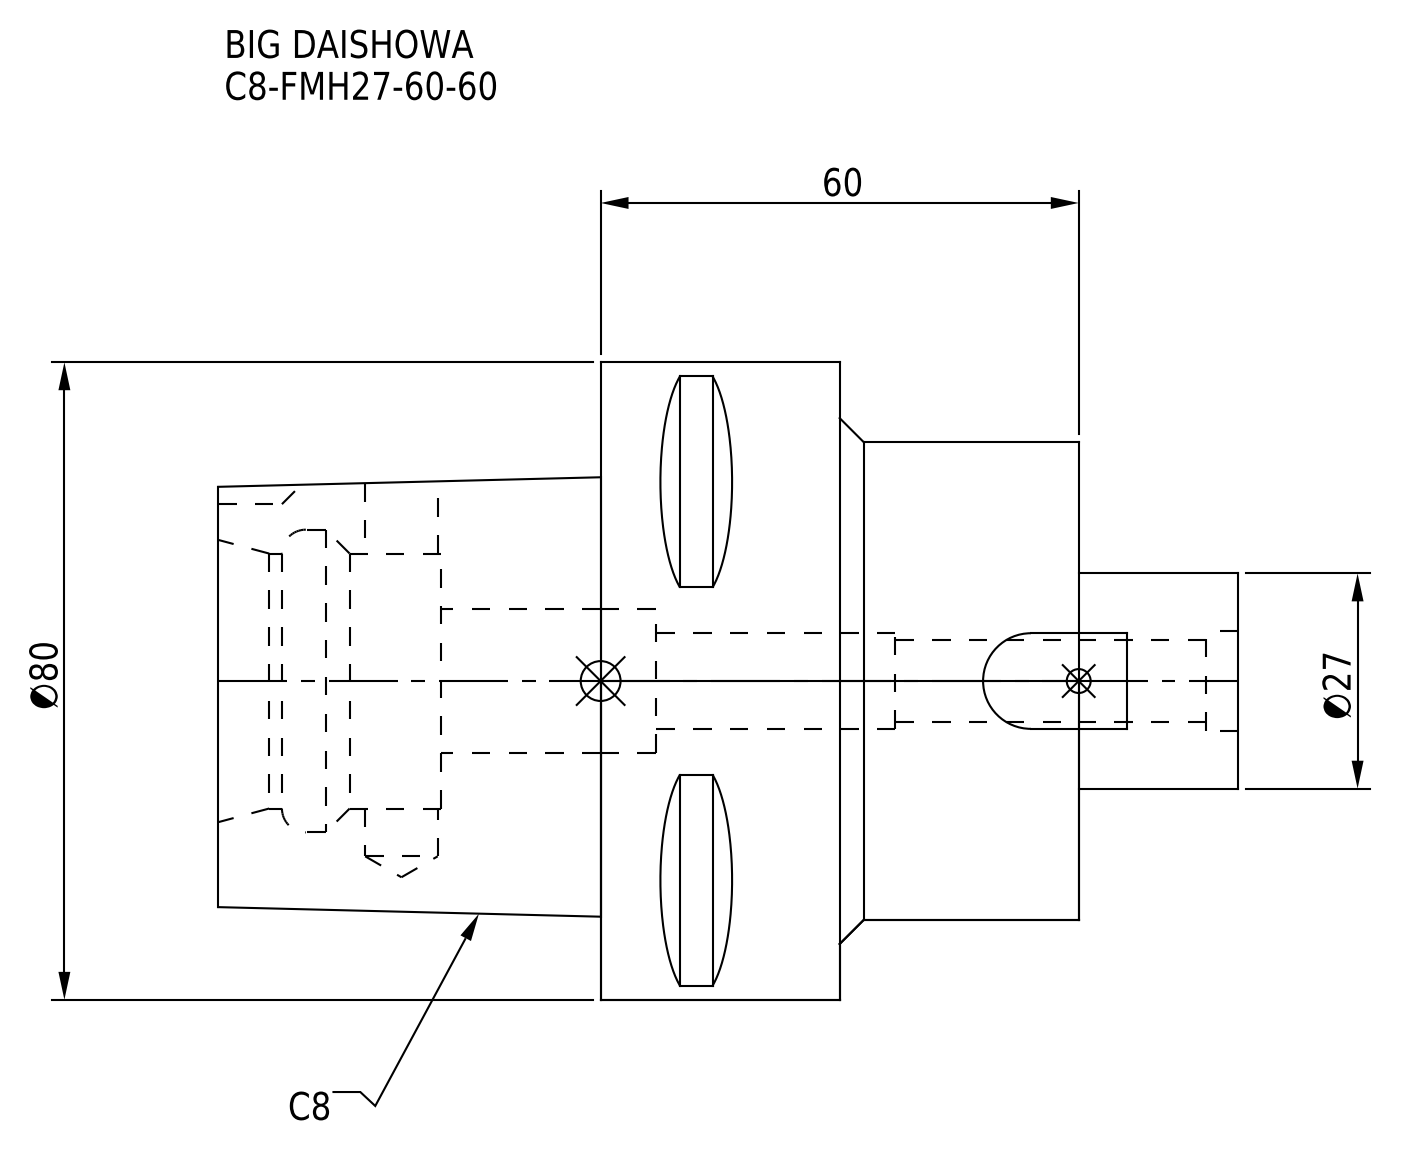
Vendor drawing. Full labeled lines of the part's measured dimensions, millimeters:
Part name (STEP PRODUCT): C8-FMH27-60-60
STEP written by: CREO PARAMETRIC BY PTC INC, 2016380 (AUTOMOTIVE_DESIGN)
Units: millimetres
Bodies: 1 solid, 78 faces (41 planar, 25 cylindrical, 12 other)
Overall size (bounding box): 128 × 80 × 80
Volume: 314 857 mm³ · Surface area: 41 020 mm²
Round holes (diameter × count): ⌀9.1 ×1, ⌀10.3 ×1, ⌀12 ×1, ⌀12.5 ×1, ⌀18 ×1, ⌀32 ×1, ⌀38 ×1
Round bosses / shafts (diameter × count): ⌀80 ×1, ⌀60 ×1, ⌀27 ×1
Partial cylindrical surfaces — rounded edges, fillets, slot ends (radius × count): R6 ×1
Main face-to-face distances: 30, 60, 108, 78, 48, 20, 50, 80, 28, 100
